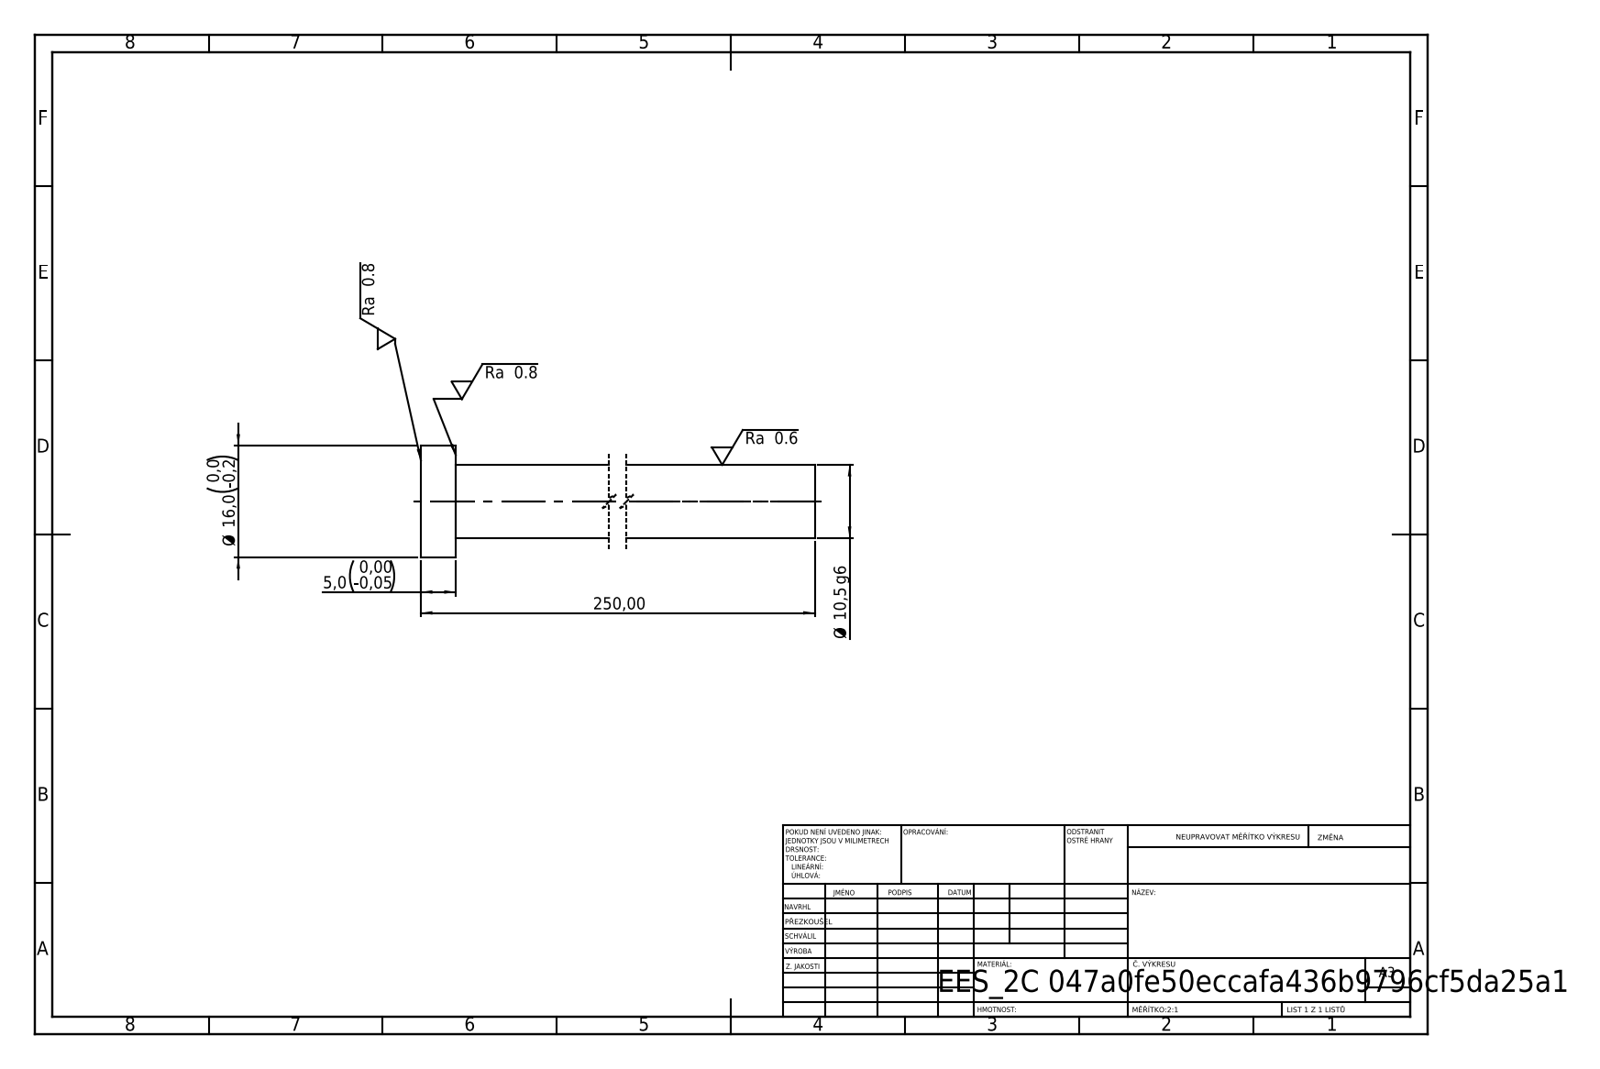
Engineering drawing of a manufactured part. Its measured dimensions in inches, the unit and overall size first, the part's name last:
Units: inches
Overall size (bounding box): 9.843 × 0.63 × 0.63
Round bosses / shafts (diameter × count): ⌀0.63 ×1, ⌀0.413 ×1
Main face-to-face distances: 0.197, 9.843, 9.646
Volume: 1.356 in³ · Surface area: 13.54 in²
Bodies: 1 solid, 7 faces (3 planar, 4 cylindrical, 0 other)
STEP written by: SolidWorks 2019 (CONFIG_CONTROL_DESIGN)
